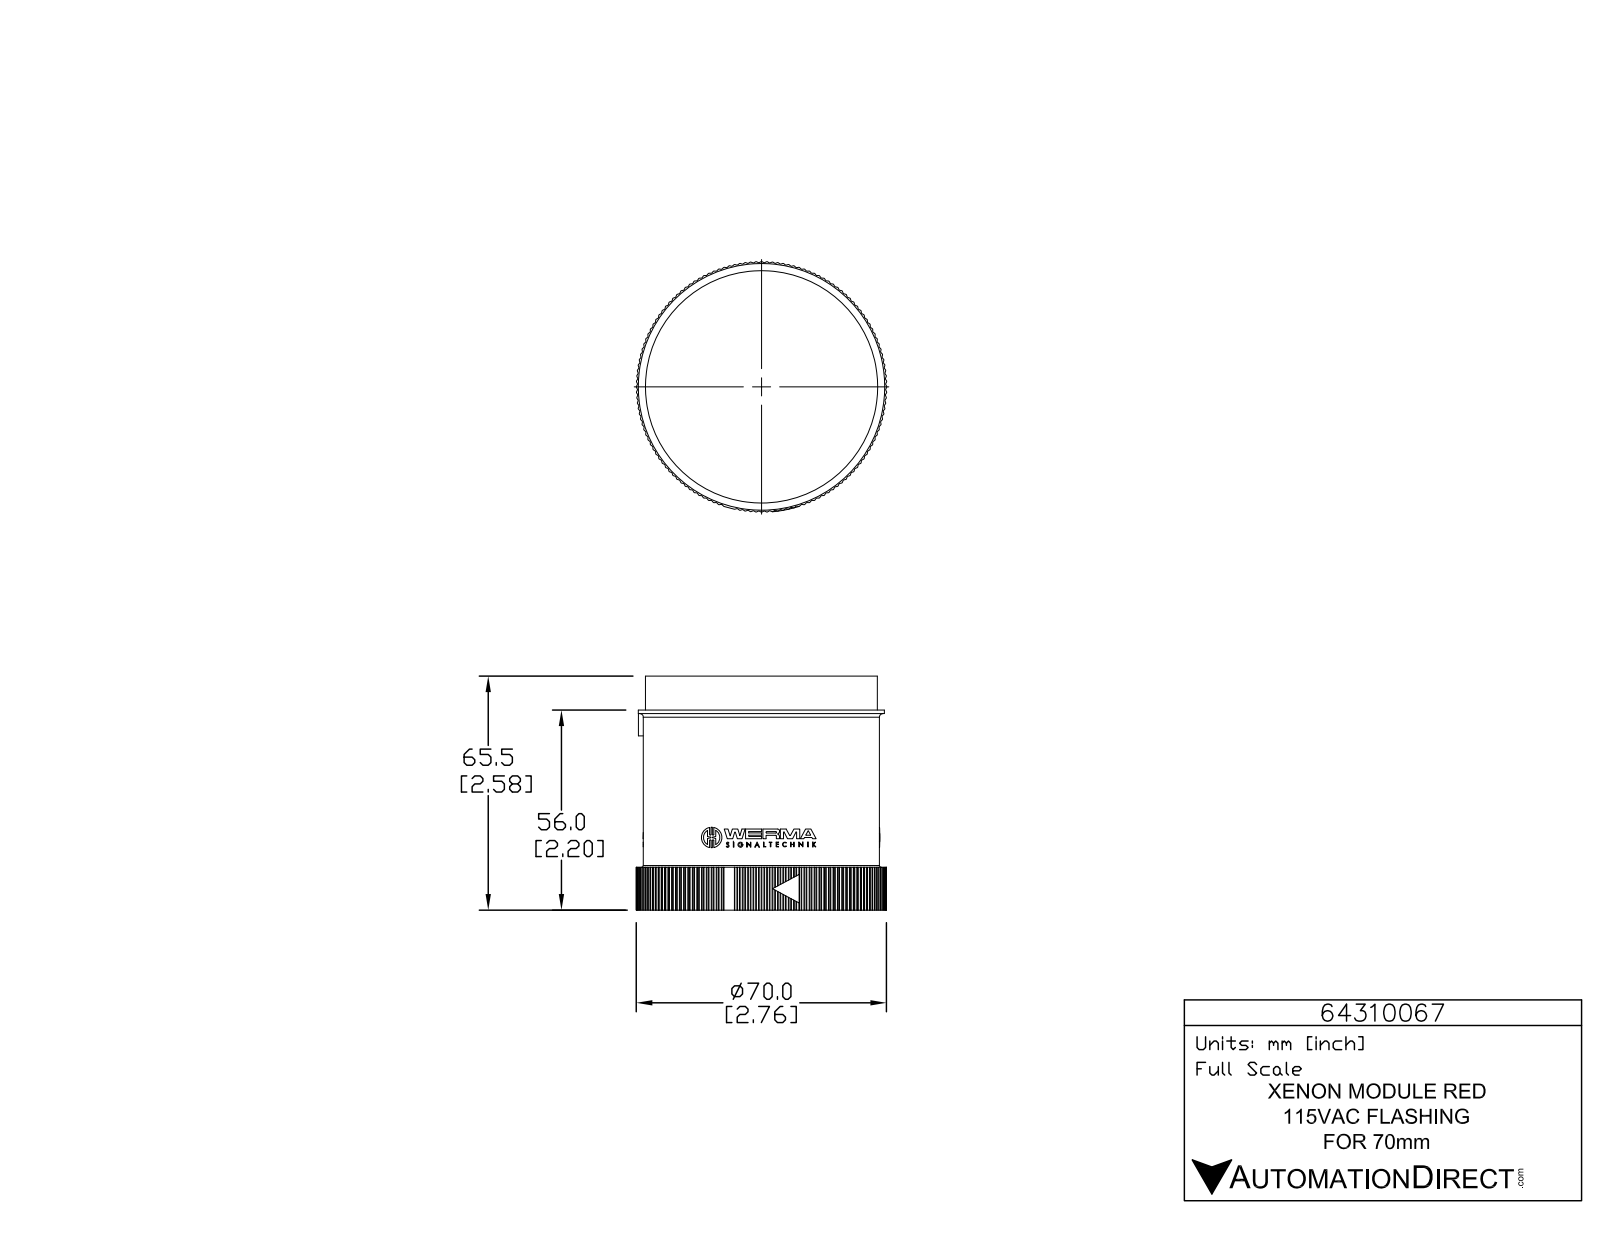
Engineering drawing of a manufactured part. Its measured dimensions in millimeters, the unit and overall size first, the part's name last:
Units: millimetres
Overall size (bounding box): 70.2 × 70.2 × 65.5
Round holes (diameter × count): ⌀1 ×3, ⌀65.4 ×1
Round bosses / shafts (diameter × count): ⌀5.7 ×3, ⌀1.4 ×3, ⌀69 ×1, ⌀66.2 ×1, ⌀65 ×1
Partial cylindrical surfaces — rounded edges, fillets, slot ends (radius × count): R0.2 ×285, R0.2 ×6, R0.2 ×6, R0.2 ×6, R3.3 ×6, R0.1 ×3, R0.1 ×3, R0.2 ×3
Main face-to-face distances: 55.9, 62.3, 9.6, 65.5, 56, 46.4, 9.5, 62.3, 12, 2.4
Volume: 197 000 mm³ · Surface area: 24 180 mm²
Bodies: 1 solid, 1400 faces (832 planar, 563 cylindrical, 5 other)
Part name (STEP PRODUCT): 64310067
STEP written by: SolidWorks 2015 (AUTOMOTIVE_DESIGN)
